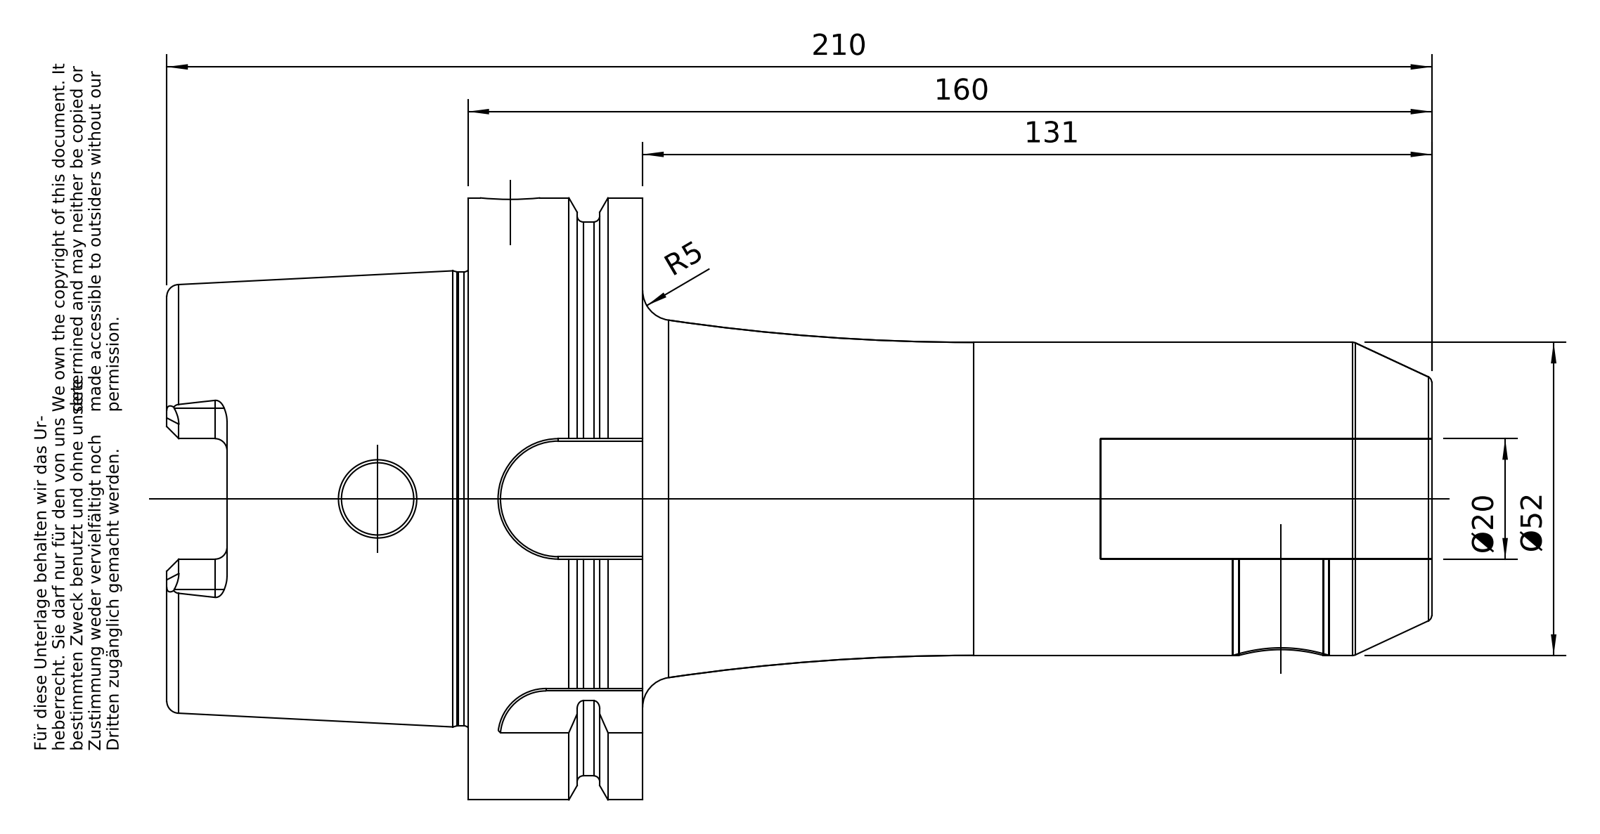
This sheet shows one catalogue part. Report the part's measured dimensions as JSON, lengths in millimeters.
{"part_name": "A100-002-20", "step_written_by": "PRO/ENGINEER BY PARAMETRIC TECHNOLOGY CORPORATION, 2010430 (CONFIG_CONTROL_DESIGN)", "units": "millimeters", "bodies": {"solids": 1, "faces": 182, "planar": 50, "cylindrical": 55, "other": 77}, "overall_size": [210, 100, 100], "volume_mm3": 521156, "surface_area_mm2": 74941, "round_holes": [[10, 1], [12, 1], [14, 1], [16, 1], [20, 1], [22.5, 1], [24, 1], [24.32, 1], [24.5, 1], [53, 1], [63, 1]], "round_bosses_or_shafts": [[100, 1], [92, 1], [75.36, 1], [52, 1]], "partial_cylinders_radius": [[2, 6], [5, 4], [8, 1], [10, 1], [11, 1]], "face_to_face_distances": [29, 12.5, 16.5, 50, 62.5, 79, 210, 160, 147.5, 131], "hole_center_spacings": [128]}
